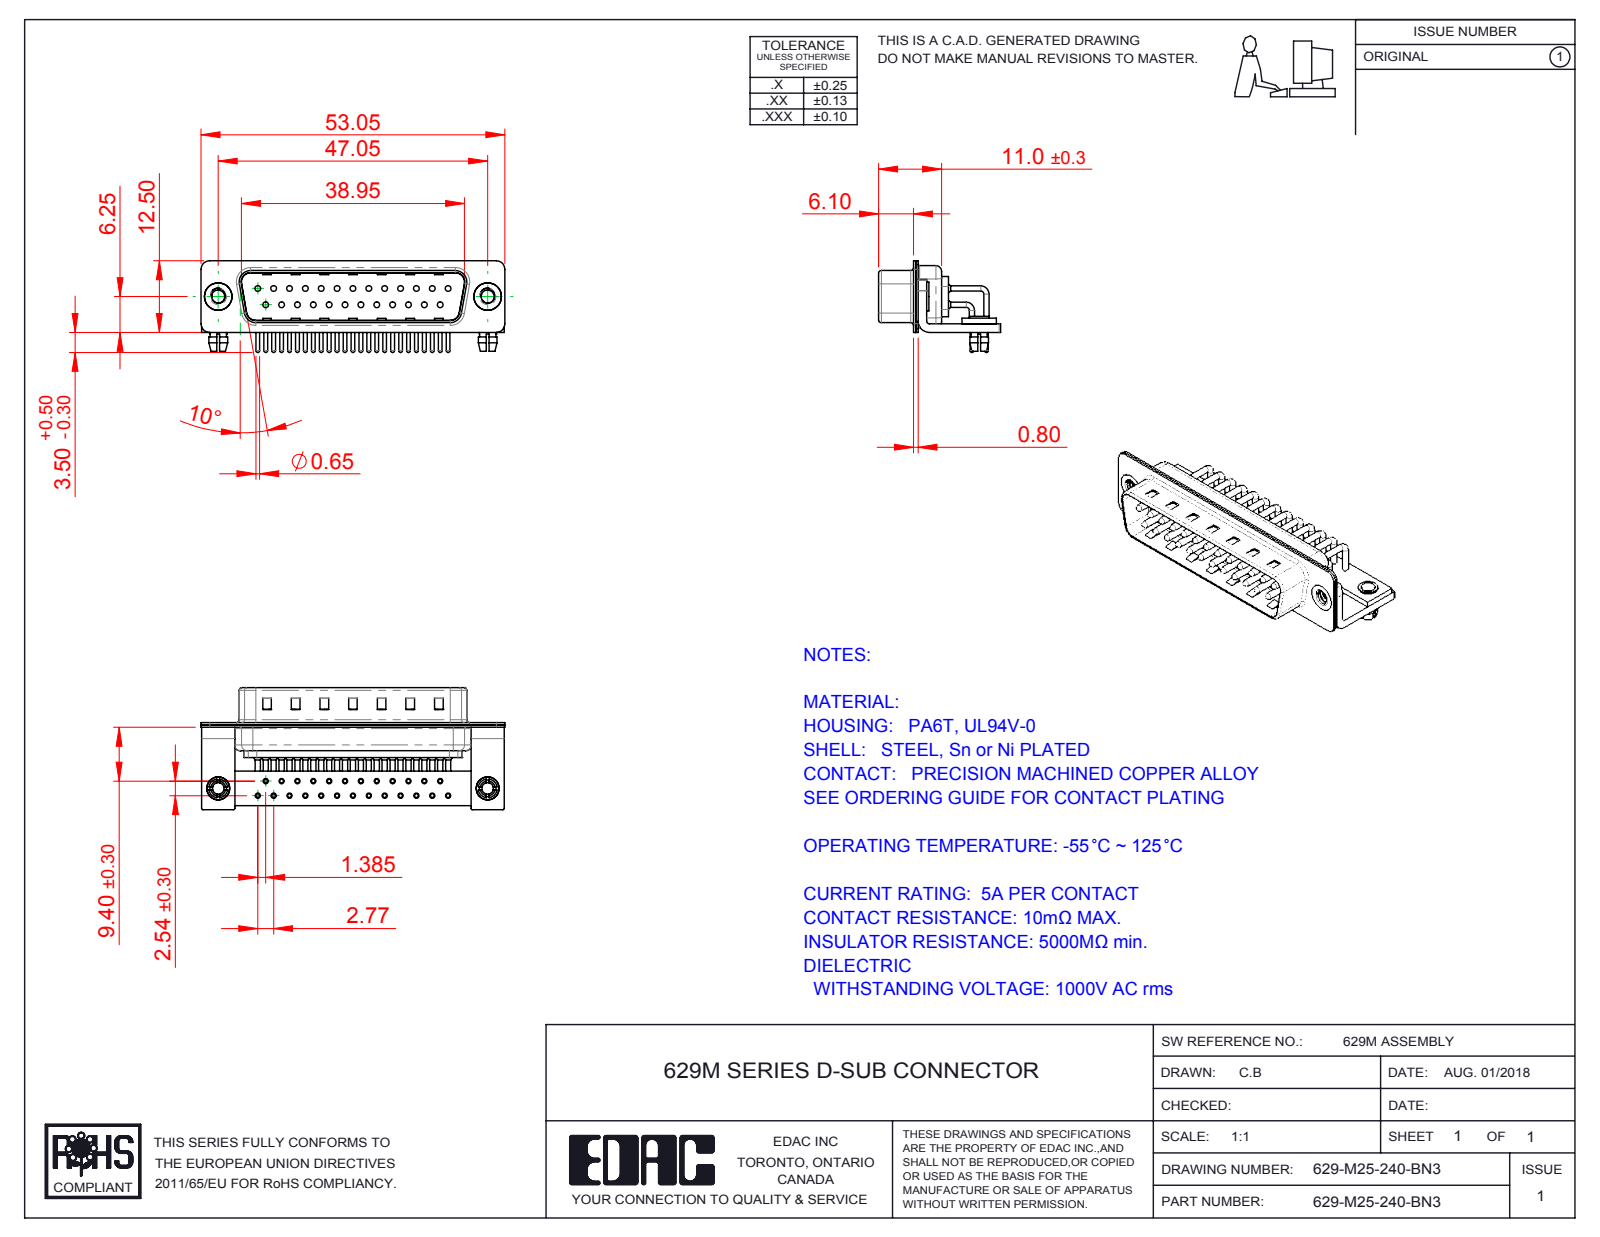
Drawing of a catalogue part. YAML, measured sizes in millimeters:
part_name: "629M 4-40 Threaded Rivet_Stabilizer; 629M Contact Row 2; 629-M25-240-BN3; 629M Contact Row 1 (+6 more)"
step_written_by: "SolidWorks 2016 (CONFIG_CONTROL_DESIGN)"
units: millimeters
bodies: {solids: 35, faces: 3318, planar: 1845, cylindrical: 1141, other: 332}
overall_size: [53.05, 21.3, 16]
volume: 3509
surface_area: 9368
round_holes:
  - {diameter: 2, count: 27}
  - {diameter: 0.9, count: 25}
  - {diameter: 1, count: 25}
  - {diameter: 1.7, count: 25}
  - {diameter: 2.26, count: 2}
  - {diameter: 2.5, count: 2}
  - {diameter: 3.2, count: 2}
  - {diameter: 4, count: 2}
  - {diameter: 4.8, count: 2}
round_bosses_or_shafts:
  - {diameter: 1.5, count: 25}
  - {diameter: 0.9, count: 25}
  - {diameter: 0.65, count: 25}
  - {diameter: 5, count: 2}
  - {diameter: 4.9, count: 2}
  - {diameter: 4, count: 2}
  - {diameter: 3.4, count: 2}
  - {diameter: 3.3, count: 2}
partial_cylinders:
  - {radius: 1.01, count: 25}
  - {radius: 0.25, count: 16}
  - {radius: 1.5, count: 16}
  - {radius: 2, count: 13}
  - {radius: 0.5, count: 9}
  - {radius: 1.6, count: 8}
  - {radius: 0.6, count: 4}
  - {radius: 0.65, count: 4}
face_to_face_distances: [0.4, 0.85, 1.25, 1.5, 0.8, 9.55, 10.4, 1, 1.9, 8.3]
hole_center_spacings: [2.77, 5.54, 8.31, 11.08, 13.85, 3.16, 4.87, 16.62]
